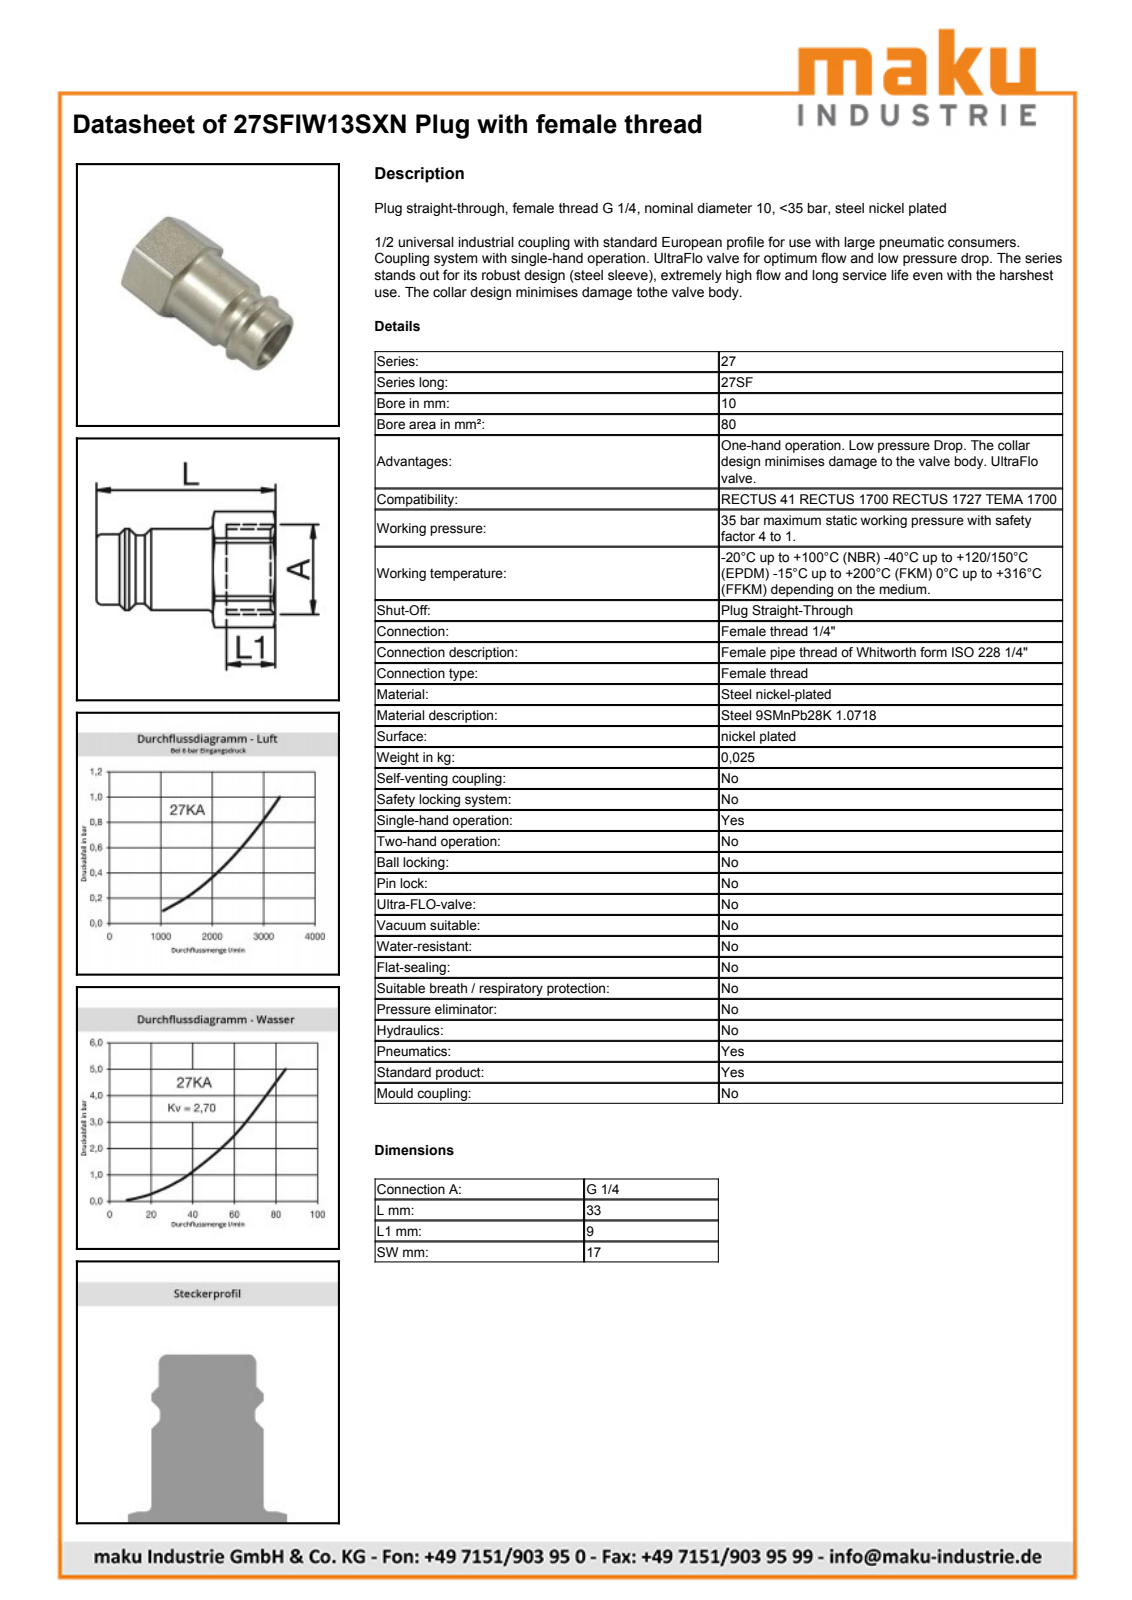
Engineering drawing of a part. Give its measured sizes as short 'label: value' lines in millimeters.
name: D106716
written by: Autodesk Inventor 2011 (AUTOMOTIVE_DESIGN)
unit: mm
bodies: 1 solid, 41 faces (9 planar, 12 cylindrical, 20 other)
size: 32.6 × 19.15 × 17
volume: 3 419 mm³; area: 2 961 mm²
holes: 1× ⌀10, 1× ⌀11.45
bosses: 1× ⌀15, 1× ⌀13, 1× ⌀12.65
rounds: 1× R9.57
face distances: 17, 9, 23.6, 32.6
